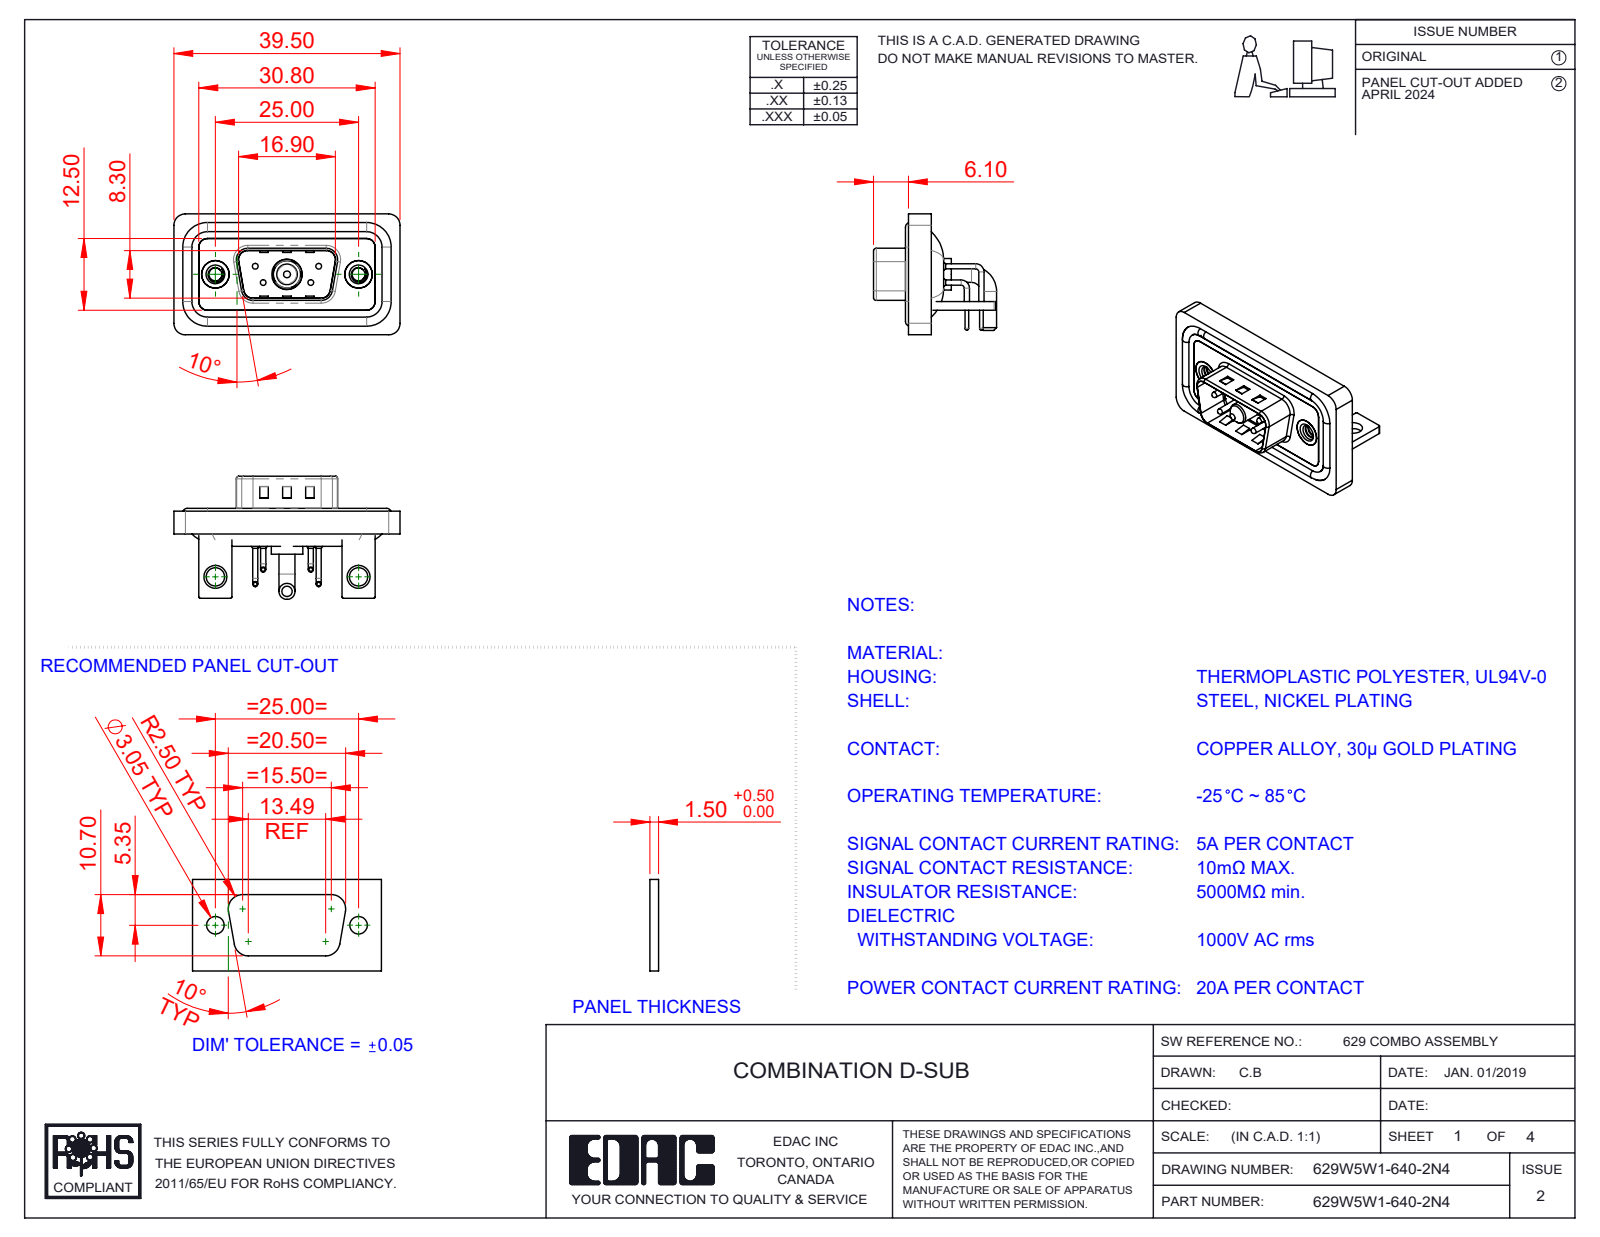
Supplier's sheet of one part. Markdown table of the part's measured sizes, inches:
| quantity | value |
| --- | --- |
| part name | 629Combo Stabilizer Bracket; 629W5W1-640-2N4; 629Combo Waterproof Housing_09 Contacts; 629Combo Housing_5W1 (+6 more) |
| STEP written by | SolidWorks 2023 (CONFIG_CONTROL_DESIGN) |
| units | inches |
| bodies | 15 solids, 934 faces (431 planar, 363 cylindrical, 140 other) |
| overall size | 1.555 × 0.846 × 0.831 |
| volume | 0.29 in³ |
| surface area | 12.01 in² |
| round holes (diameter × count) | 0.03 × 4, 0.063 × 4, 0.079 × 4, 0.089 × 2, 0.126 × 2, 0.157 × 2, 0.189 × 2, 0.197 × 2, 0.191 × 1, 0.209 × 1 |
| round bosses / shafts (diameter × count) | 0.035 × 8, 0.063 × 4, 0.059 × 4, 0.039 × 4, 0.026 × 4, 0.193 × 2, 0.11 × 2, 0.217 × 1 |
| partial cylindrical surfaces (radius × count) | 0.079 × 19, 0.059 × 18, 0.01 × 16, 0.02 × 9, 0.063 × 8, 0.024 × 4, 0.026 × 4, 0.035 × 4 |
| main face-to-face distances | 0.016, 0.059, 0.031, 0.114, 0.043, 0.083, 0.047, 0.063, 0.098, 0.146 |
| hole center spacings | 0.124, 0.225, 0.28, 0.492, 0.713, 0.984, 0.173, 0.173 |
